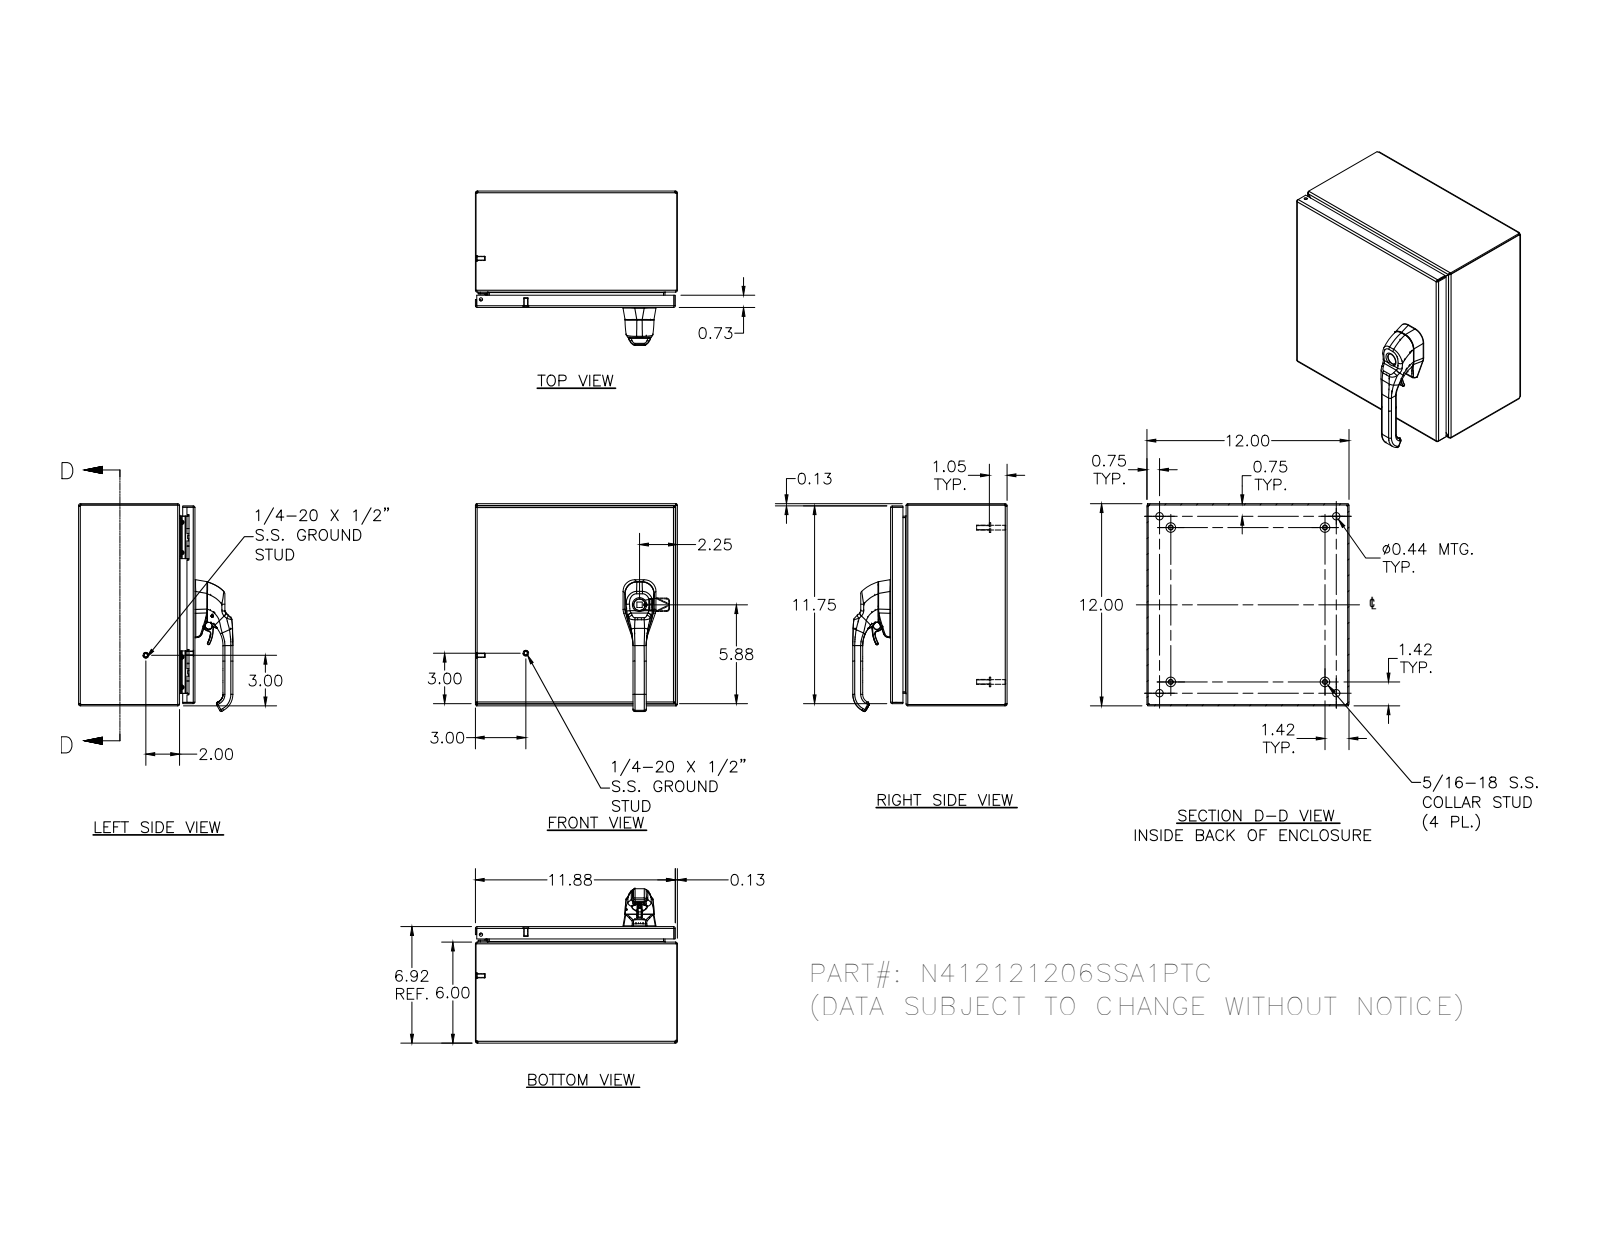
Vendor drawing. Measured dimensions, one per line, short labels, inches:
name: N412121206SSA1PTC; N412121206SSA1PTCBKP; N4121212SSA1PTCLID; HFW328176 (+8 more)
written by: Autodesk Inventor 2012 (AUTOMOTIVE_DESIGN)
unit: in
bodies: 41 solids, 2784 faces (882 planar, 1037 cylindrical, 865 other)
size: 12.34 × 12 × 9.166
volume: 57.53 in³; area: 1 469 in²
holes: 5× ⌀0.188, 4× ⌀0.093, 4× ⌀0.152, 4× ⌀0.167, 4× ⌀0.172, 4× ⌀0.437, 3× ⌀0.213, 3× ⌀0.281, 2× ⌀0.156, 2× ⌀0.315, 2× ⌀0.402, 2× ⌀0.413
bosses: 10× ⌀0.25, 4× ⌀0.563, 4× ⌀0.36, 4× ⌀0.32, 4× ⌀0.3, 4× ⌀0.275, 4× ⌀0.256, 4× ⌀0.164
rounds: 173× R0.02, 101× R0.012, 30× R0.031, 26× R0.05, 21× R0.019, 20× R0.105, 18× R0.016, 14× R0.079
face distances: 0.074, 11.926, 6.843, 12, 11.852, 6.917, 6.769, 5.926, 0.917, 0.125
hole spacings: 7.996, 10.5, 0.017, 0.66, 8.656, 9.756, 0.019, 0.5
